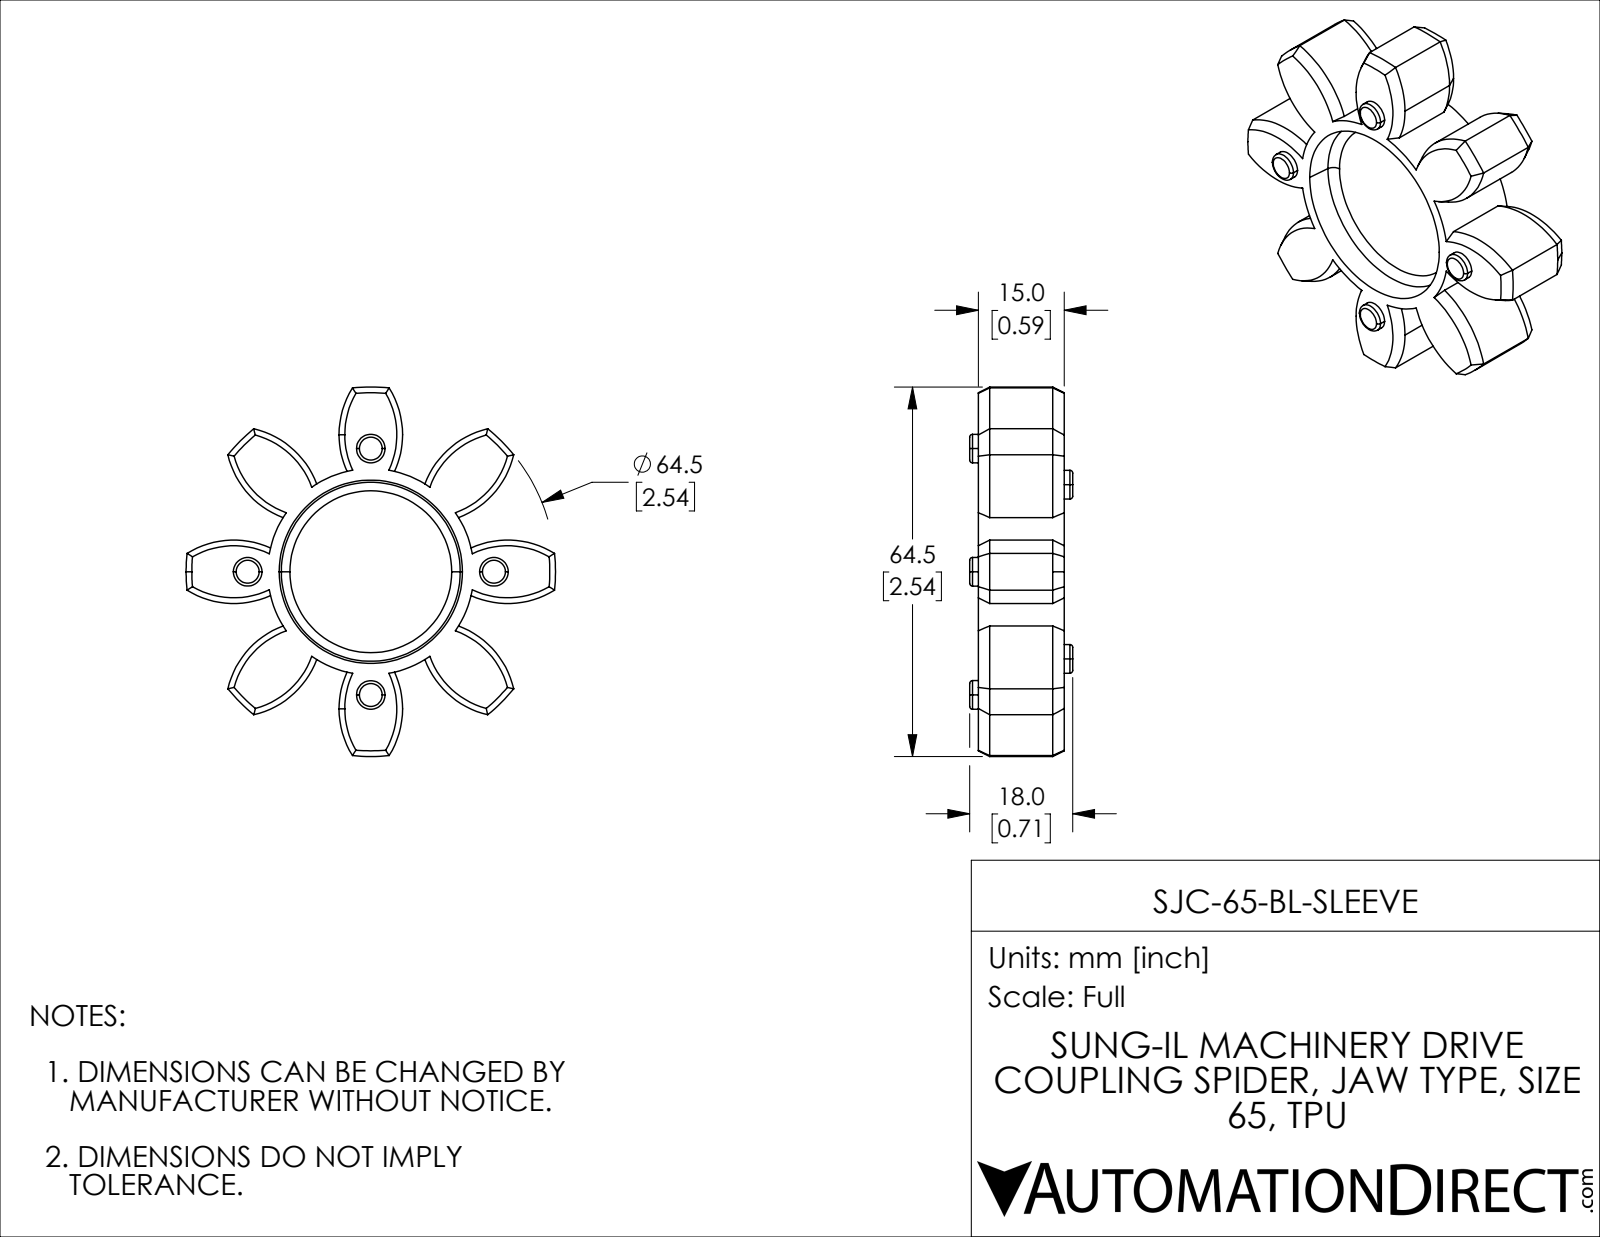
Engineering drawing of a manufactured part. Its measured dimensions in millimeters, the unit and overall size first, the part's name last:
Units: millimetres
Overall size (bounding box): 64.5 × 64.5 × 18
Round bosses / shafts (diameter × count): ⌀5 ×8
Partial cylindrical surfaces — rounded edges, fillets, slot ends (radius × count): R15.45 ×8, R18 ×1, R32.25 ×1
Main face-to-face distances: 5.5, 9.5, 15, 4, 1.5, 7, 11, 16.5, 18
Volume: 23 398 mm³ · Surface area: 10 008 mm²
Bodies: 1 solid, 141 faces (12 planar, 51 cylindrical, 78 other)
Part name (STEP PRODUCT): SJC-65-BL-SLEEVE
STEP written by: SolidWorks 2021 (CONFIG_CONTROL_DESIGN)
